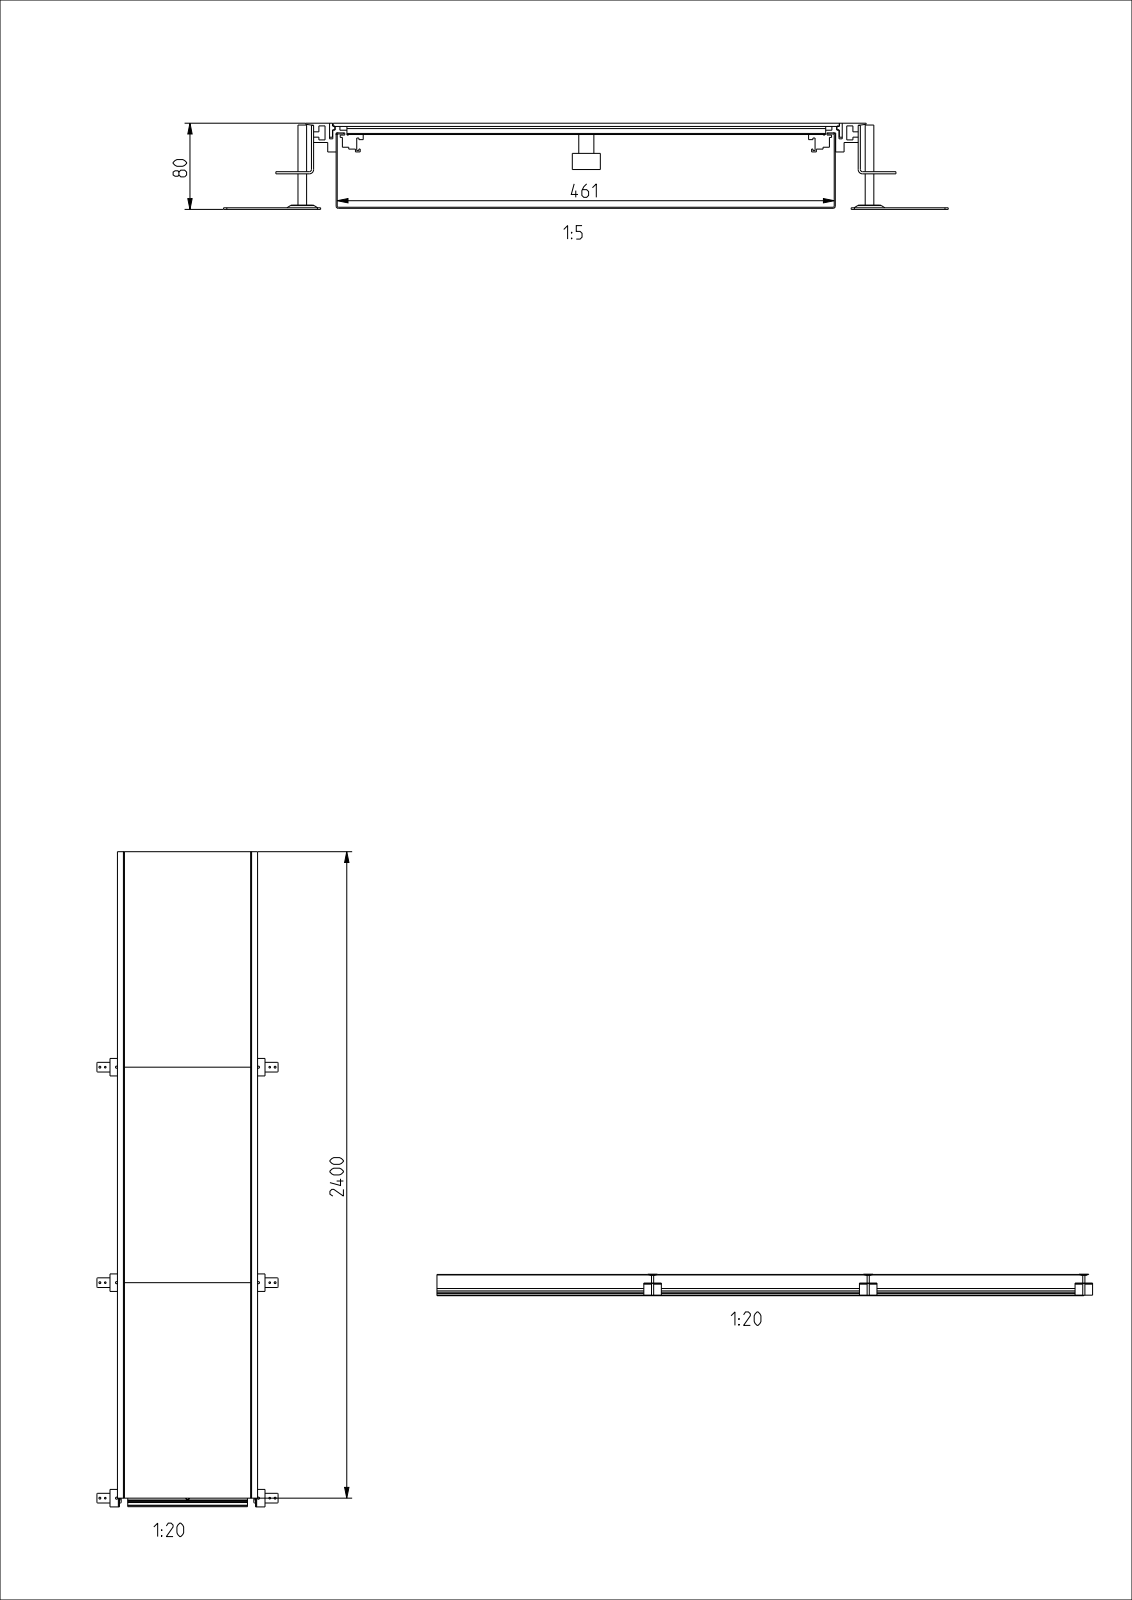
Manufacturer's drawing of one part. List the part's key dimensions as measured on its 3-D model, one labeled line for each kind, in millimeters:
Part name (STEP PRODUCT): U05644KUN; U05650KUN; U05647KUN; U05826KUN (+8 more)
STEP written by: CREO PARAMETRIC BY PTC INC, 2020281 (AUTOMOTIVE_DESIGN)
Units: millimetres
Bodies: 61 solids, 1036 faces (606 planar, 358 cylindrical, 72 other)
Overall size (bounding box): 2432.5 × 672.13 × 80
Volume: 9 136 000 mm³ · Surface area: 7 587 000 mm²
Round holes (diameter × count): ⌀7 ×15, ⌀8 ×9, ⌀10 ×9, ⌀6 ×6, ⌀8.5 ×6, ⌀11.5 ×6, ⌀17.5 ×6, ⌀23 ×6
Round bosses / shafts (diameter × count): ⌀26 ×9, ⌀14 ×9, ⌀11.9 ×9, ⌀20 ×6, ⌀8 ×6
Partial cylindrical surfaces — rounded edges, fillets, slot ends (radius × count): R2 ×96, R3 ×24, R0.5 ×20, R1 ×4, R4 ×2
Main face-to-face distances: 1, 3, 76, 79, 75, 78, 462, 7.5, 6.5, 68.5
Hole centre spacings: 800, 1600, 800.25, 801.1, 802.4, 981.21, 992.92, 1018.36
